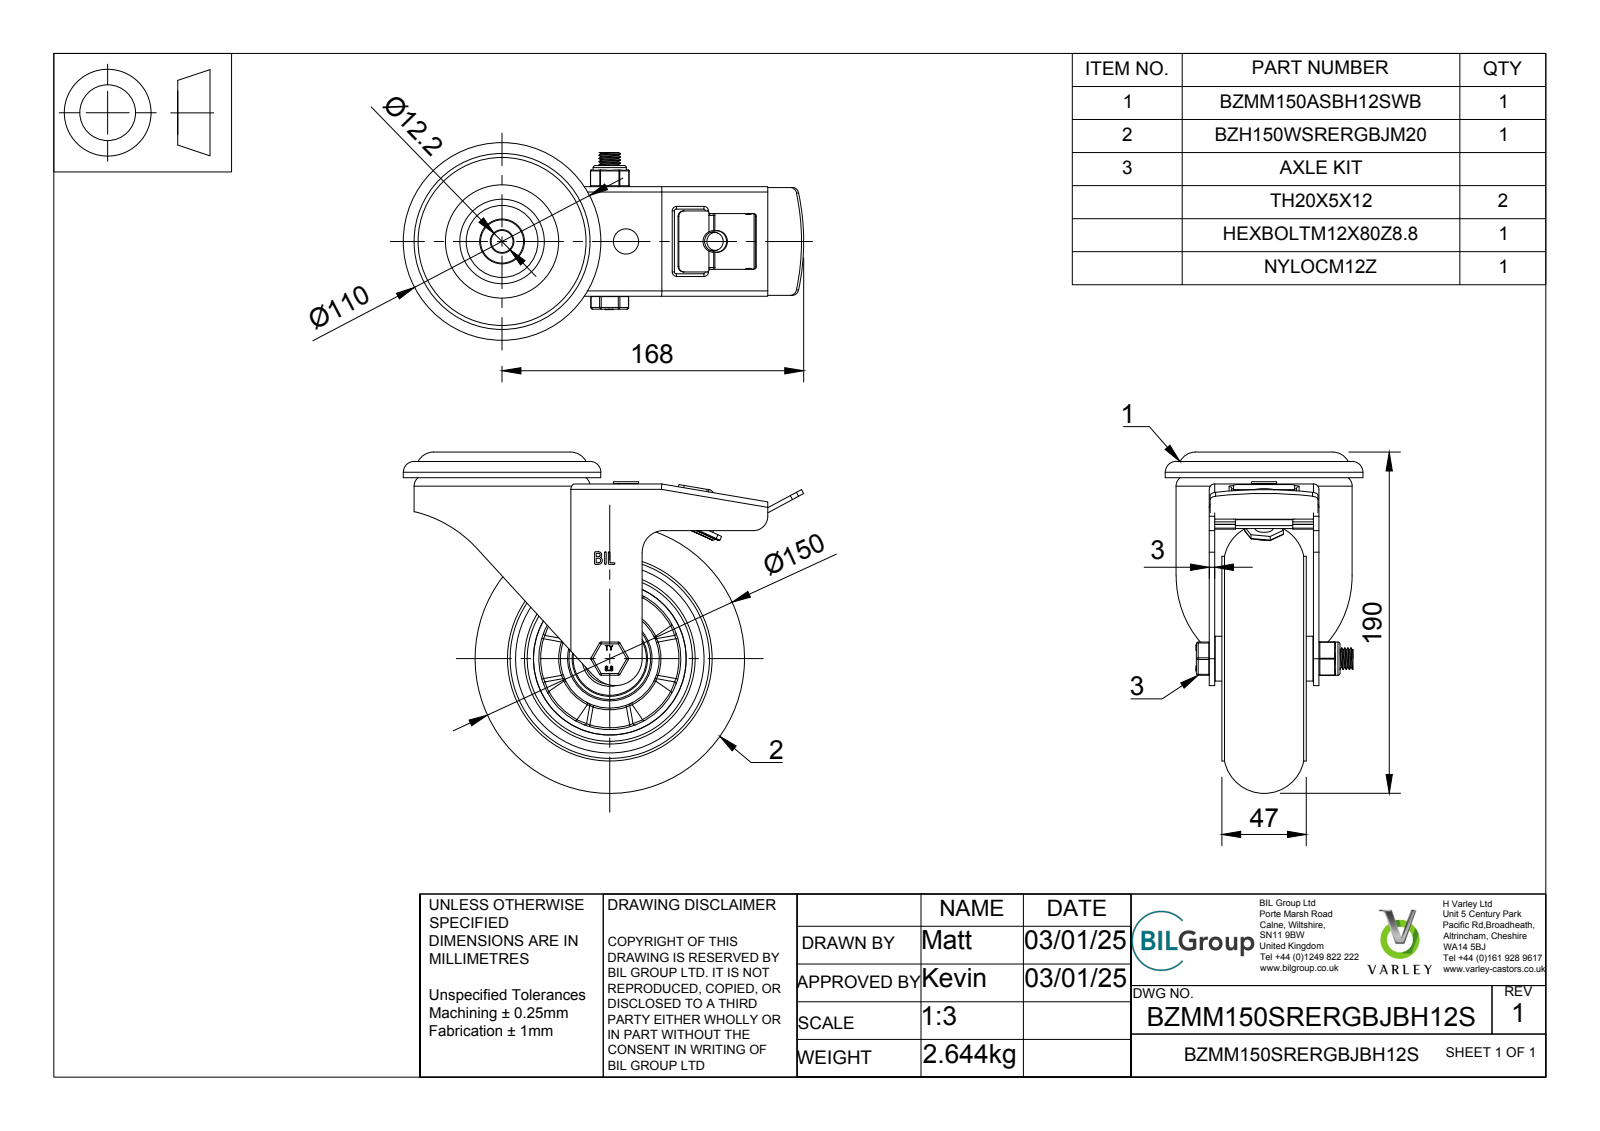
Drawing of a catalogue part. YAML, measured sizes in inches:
part_name: "BZMM150SRERGBJBH12S v3; BZH150WSRERGBJM20 v1; 55 SHORE A ELASTIC RUBBER TYRE; ALUMINIUM RIM (+7 more)"
step_written_by: "Autodesk Translation Framework v13.20.0.188 (AP242_MANAGED_MODEL_BASED_3D_ENGINEERING_MIM_LF)"
units: inches
bodies: {solids: 41, faces: 1448, planar: 578, cylindrical: 264, other: 606}
overall_size: [8.78, 7.48, 4.331]
volume: 45.01
surface_area: 417.9
round_holes:
  - {diameter: 0.315, count: 2}
  - {diameter: 3.622, count: 2}
  - {diameter: 0.472, count: 1}
  - {diameter: 0.476, count: 1}
  - {diameter: 0.48, count: 1}
  - {diameter: 0.492, count: 1}
  - {diameter: 0.551, count: 1}
  - {diameter: 0.787, count: 1}
  - {diameter: 1.122, count: 1}
  - {diameter: 1.213, count: 1}
  - {diameter: 1.319, count: 1}
  - {diameter: 1.339, count: 1}
round_bosses_or_shafts:
  - {diameter: 0.984, count: 2}
  - {diameter: 4.488, count: 1}
  - {diameter: 4.331, count: 1}
  - {diameter: 3.74, count: 1}
  - {diameter: 3.031, count: 1}
  - {diameter: 2.165, count: 1}
  - {diameter: 1.606, count: 1}
  - {diameter: 1.575, count: 1}
partial_cylinders:
  - {radius: 0.02, count: 24}
  - {radius: 0.039, count: 18}
  - {radius: 0.059, count: 12}
  - {radius: 0.118, count: 8}
  - {radius: 0.079, count: 3}
  - {radius: 0.098, count: 3}
  - {radius: 0.157, count: 2}
  - {radius: 0.236, count: 2}
face_to_face_distances: [0.118, 2.283, 0.059, 0.315, 0.098, 0.187, 0.069, 0.433, 0.197, 0.128]
hole_center_spacings: [2.717]
